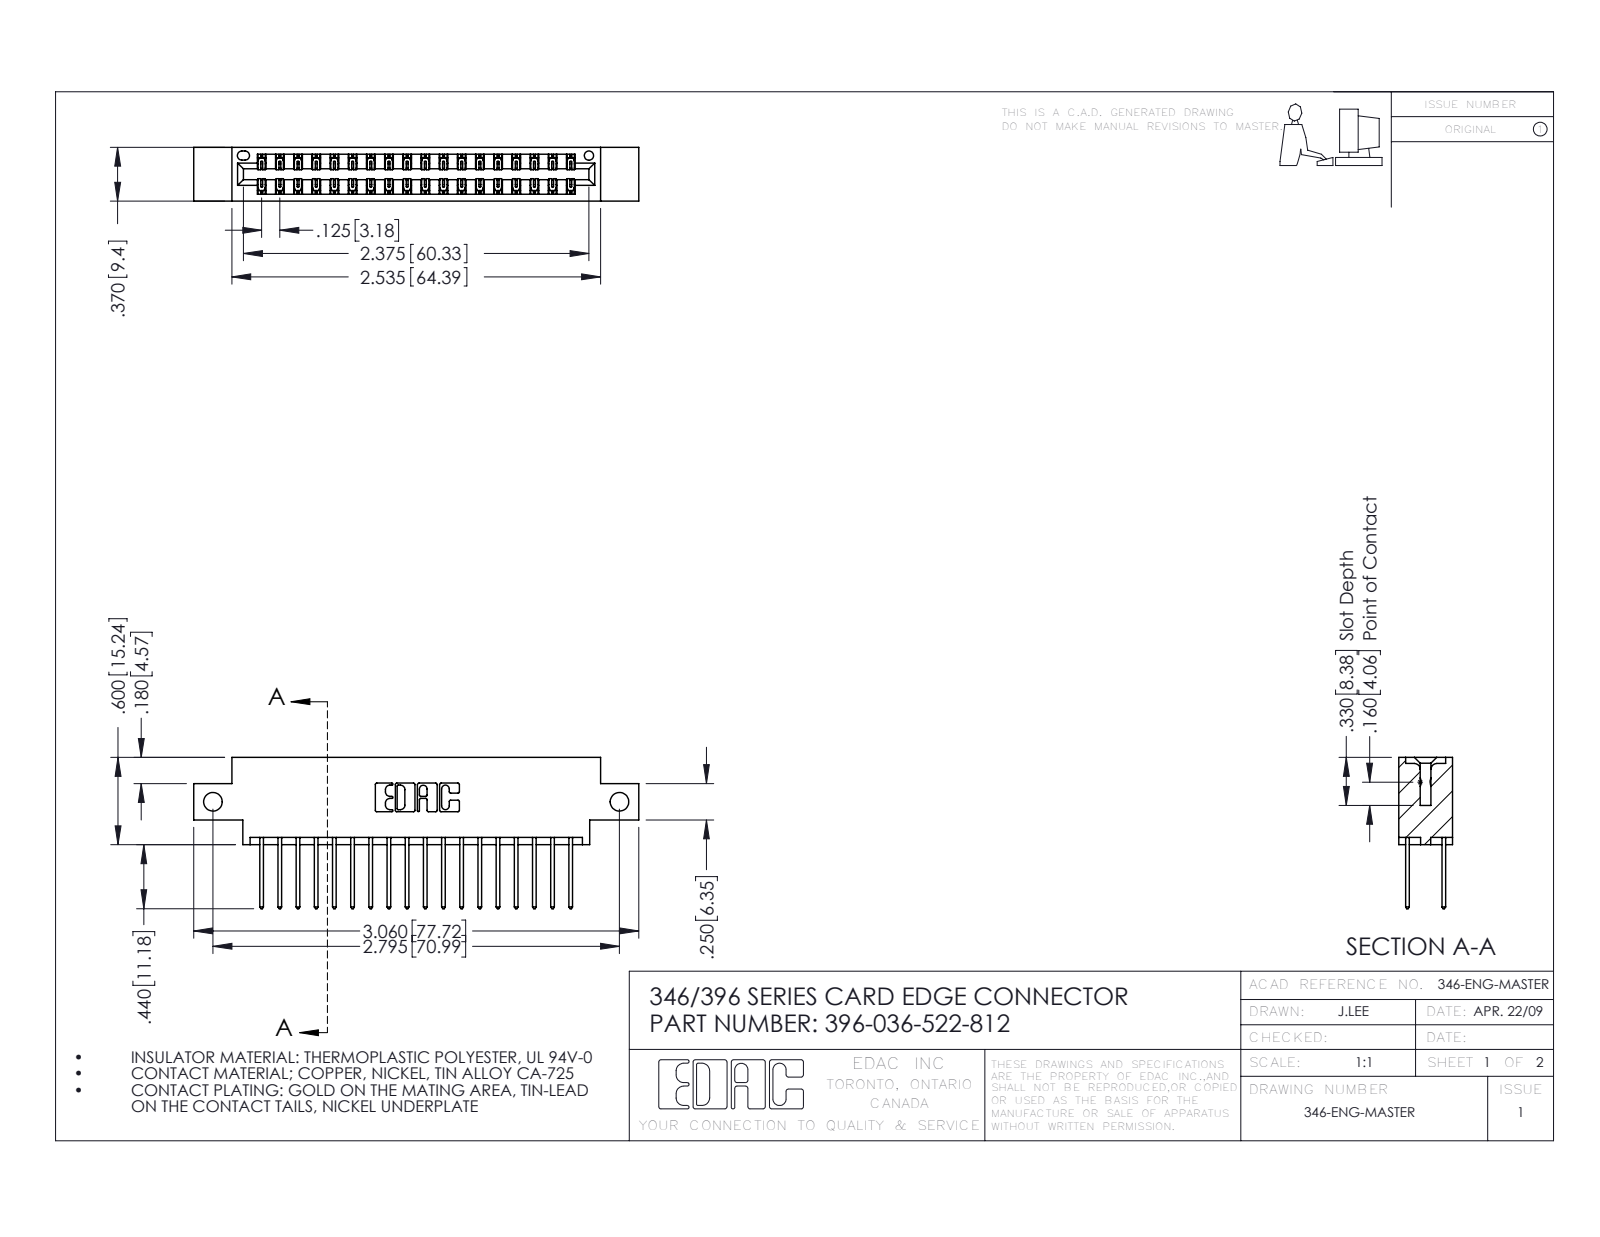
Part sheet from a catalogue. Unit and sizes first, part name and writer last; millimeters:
Units: millimetres
Overall size (bounding box): 77.7 × 26.4 × 9.4
Round holes (diameter × count): ⌀3.3 ×2, ⌀1.6 ×1
Partial cylindrical surfaces — rounded edges, fillets, slot ends (radius × count): R0.2 ×54, R0.3 ×36, R0.3 ×22, R0.2 ×6, R0.8 ×6, R0.7 ×3, R0.4 ×2, R0.6 ×2
Main face-to-face distances: 1.2, 8.2, 6.4, 9.4, 1.8, 7.6, 0.6, 7, 3.8, 5.6
Hole centre spacings: 71
Volume: 7 240 mm³ · Surface area: 10 050 mm²
Bodies: 37 solids, 1998 faces (1340 planar, 658 cylindrical, 0 other)
Part name (STEP PRODUCT): 346 Part_0.170 Offset - Side Mount; 396-036-522-812; 345-292-001_345-293-122
STEP written by: SolidWorks 2016 (CONFIG_CONTROL_DESIGN)
